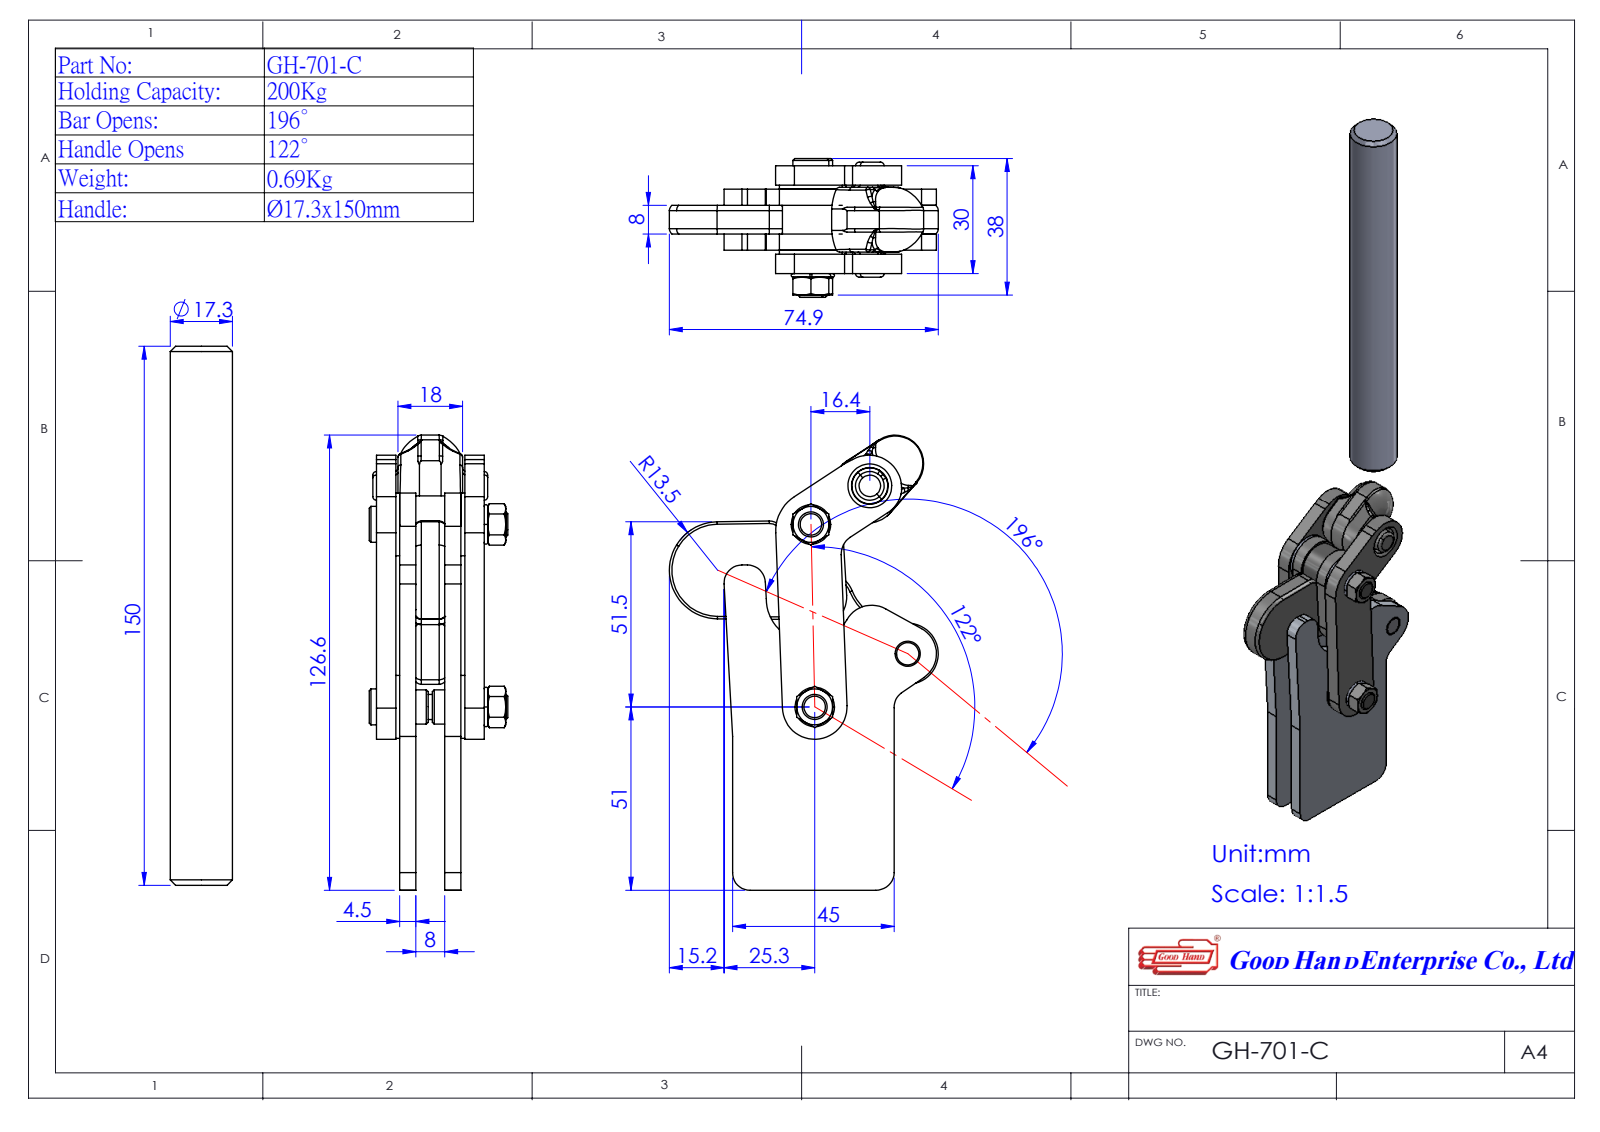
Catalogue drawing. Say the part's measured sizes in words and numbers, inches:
The part is named "1701C14; 3700108-1^GH-701-C(簡化); GH-701-C(簡化); 4702C152 (+3 more)". Its 3-D file was written by "SolidWorks 2016 (AUTOMOTIVE_DESIGN)". It is 10 solids with 453 faces: 216 planar, 183 cylindrical and 54 other. Overall it measures 10.917 by 2.911 by 1.504 inches. Its volume is 5.509 cubic inches and its surface area 83.67 square inches. Round holes: 4 of diameter 0.276, 4 of diameter 0.315, 2 of diameter 0.197, 1 of diameter 0.547. Round bosses or shafts: 4 of diameter 0.274, 2 of diameter 0.394, 1 of diameter 0.709, 1 of diameter 0.689, 1 of diameter 0.681, 1 of diameter 0.626. Partial cylindrical surfaces (rounded edges, fillets, slot ends): 16 of radius 0.079, 3 of radius 0.315, 2 of radius 0.197, 2 of radius 0.335, 2 of radius 0.344, 2 of radius 0.354, 2 of radius 0.374, 1 of radius 0.142. The main face-to-face distances are 0.177, 0.492, 0.315, 0.669, 0.047, 0.224, 0.539, 0.717, 0.213, 0.26. The hole center spacings are 2, 0.772, 0.773, 0.799, 0.799, 1.174, 1.189, 1.202.
